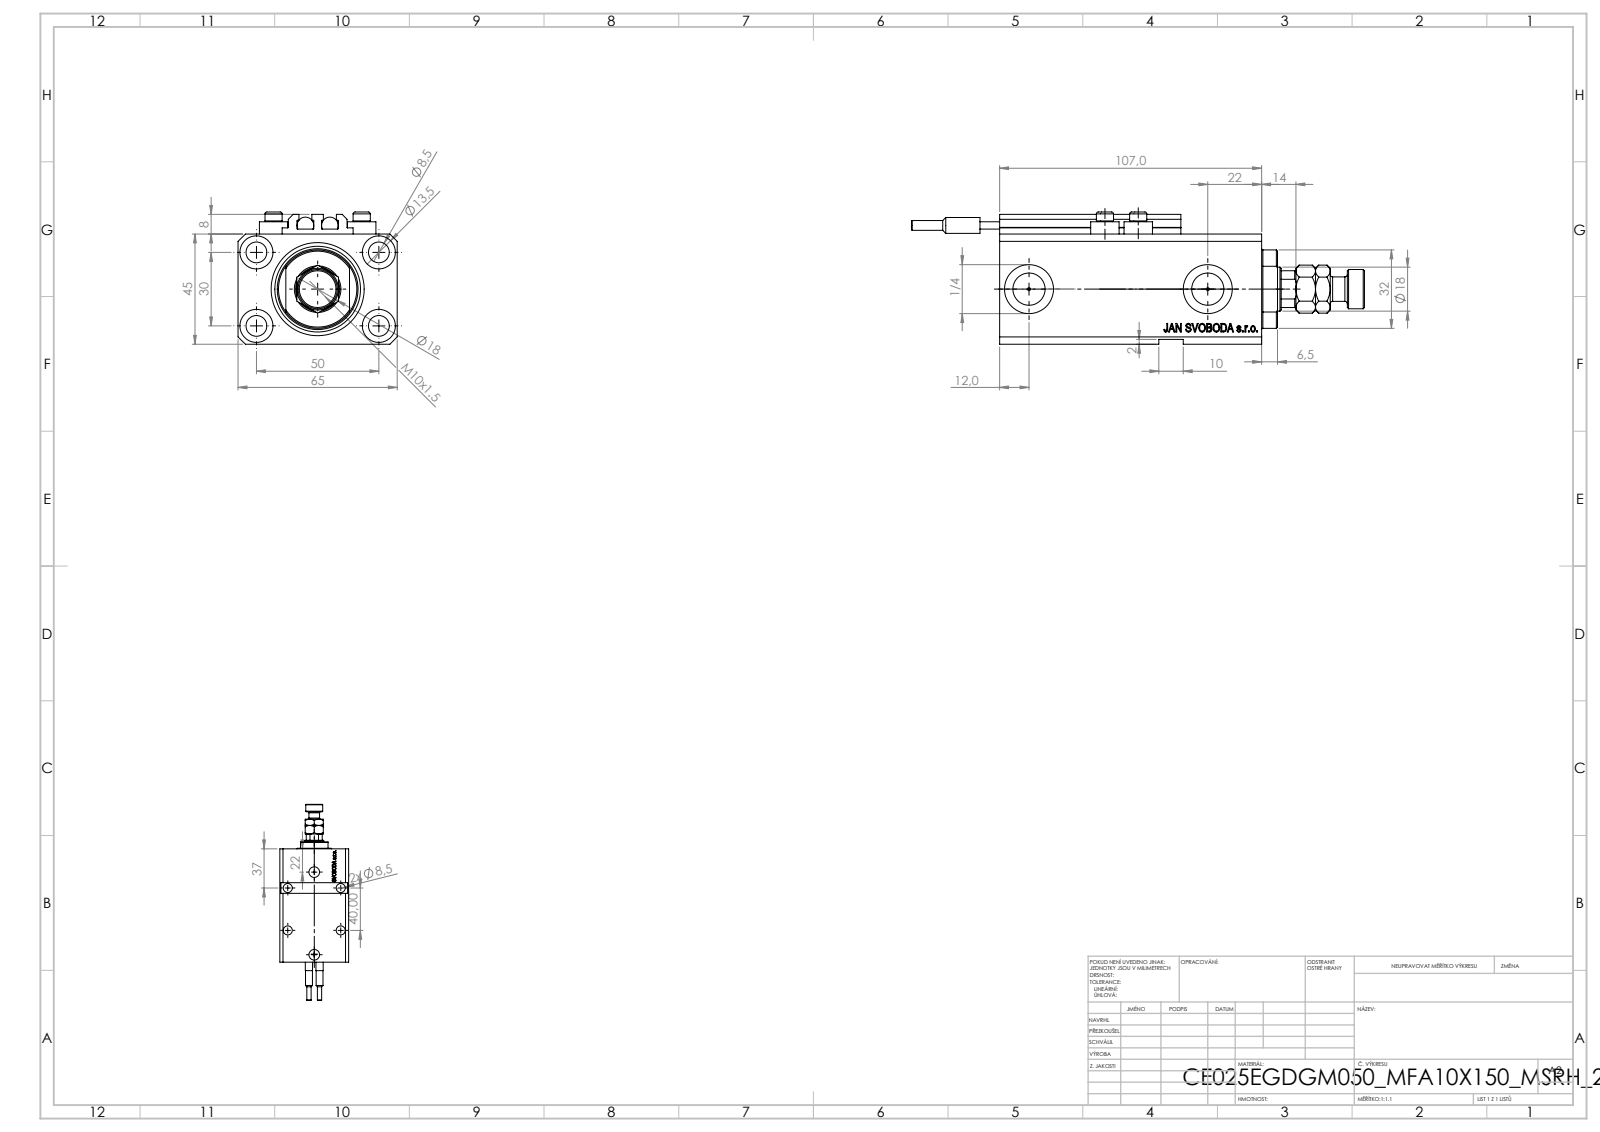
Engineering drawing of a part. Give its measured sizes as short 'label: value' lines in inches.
name: MFA; V250CE_E_Body; ALLEN BOLT V250CE; SWITCH_V250CE (+2 more)
written by: SolidWorks 2019 (CONFIG_CONTROL_DESIGN)
unit: in
bodies: 11 solids, 1207 faces (563 planar, 174 cylindrical, 470 other)
size: 7.283 × 2.559 × 2.126
volume: 17.01 in³; area: 128.4 in²
holes: 9× ⌀0.335, 4× ⌀0.049, 4× ⌀0.157, 4× ⌀0.531, 2× ⌀0.394, 2× ⌀0.518, 2× ⌀0.787, 1× ⌀0.709, 1× ⌀0.984, 1× ⌀1.496
bosses: 4× ⌀0.457, 4× ⌀0.276, 2× ⌀0.268, 2× ⌀0.256, 2× ⌀0.157, 1× ⌀0.63, 1× ⌀0.394
rounds: 10× R0.008, 1× R0.335, 1× R0.63
face distances: 1.772, 2.559, 0.551, 0.079, 1.85, 3.661, 0.118, 4.213, 0.945, 0.272
hole spacings: 1.148, 1.969, 0.535, 0.581, 0.595, 1.083, 1.098, 1.181
